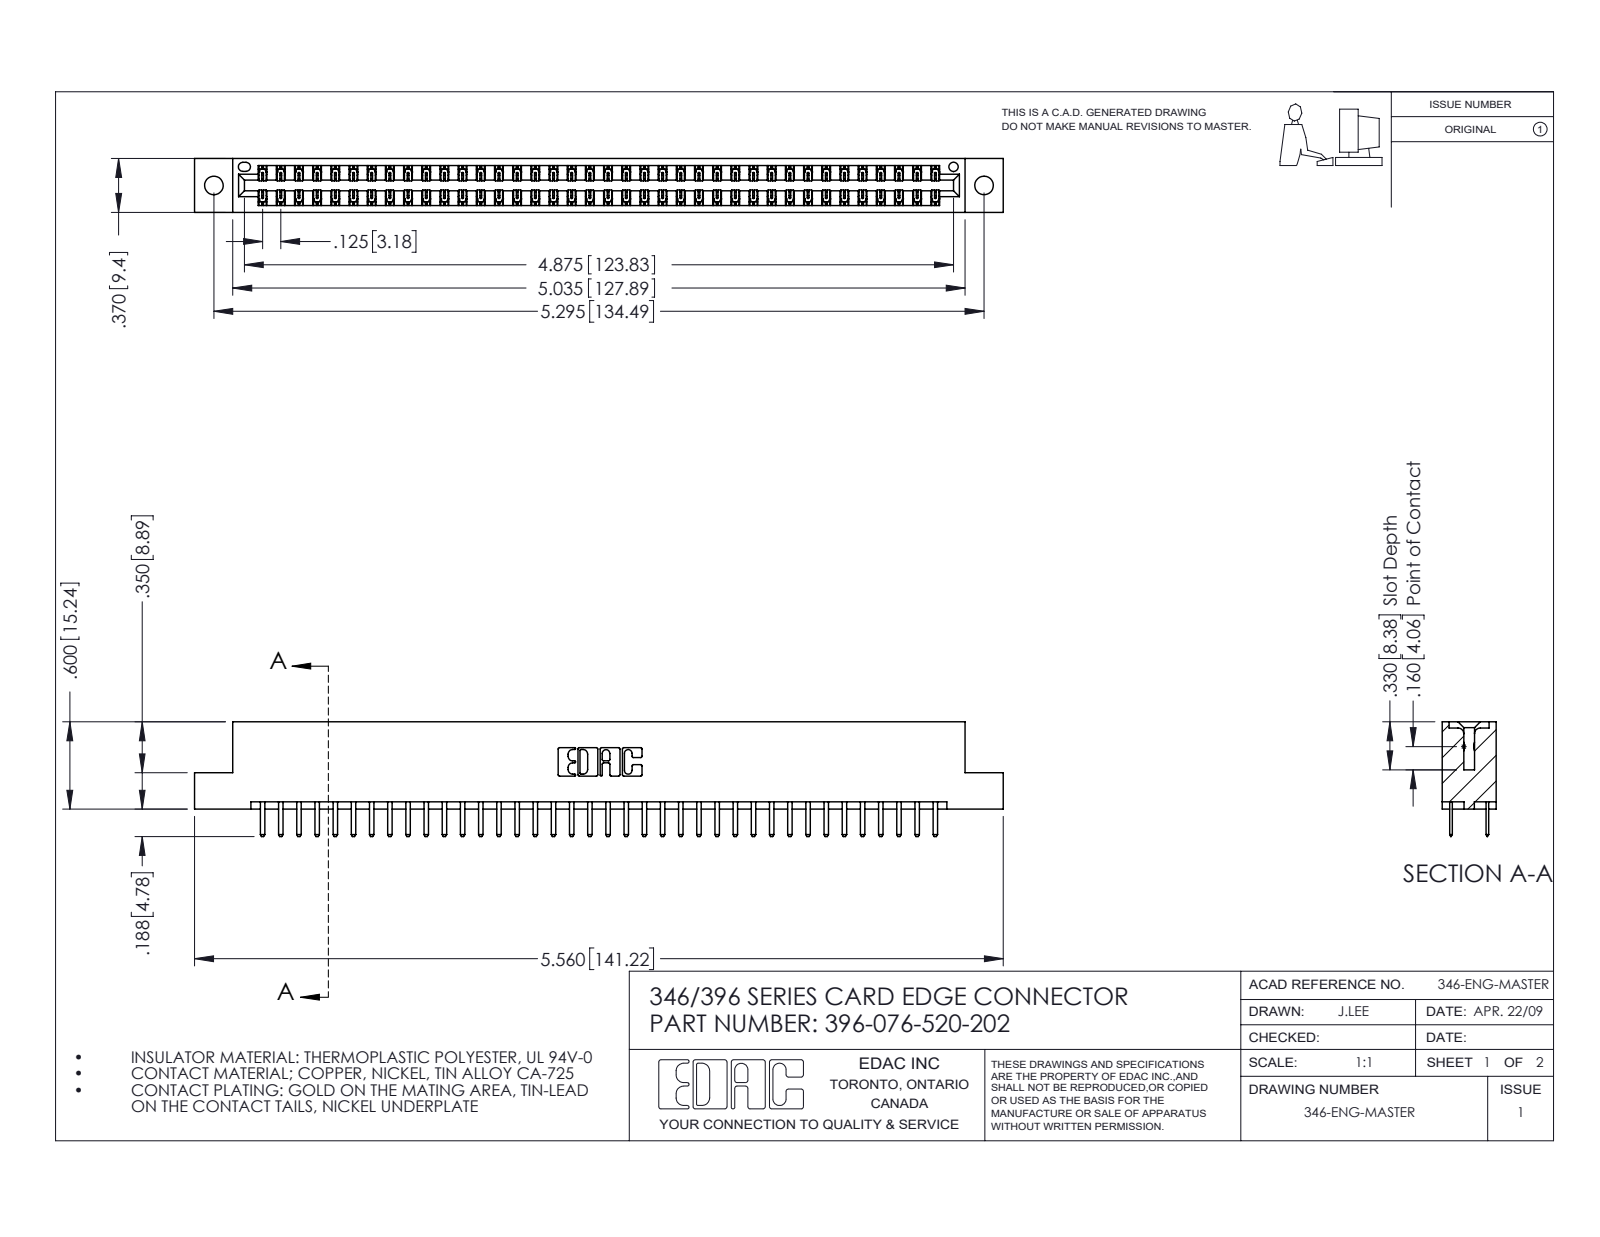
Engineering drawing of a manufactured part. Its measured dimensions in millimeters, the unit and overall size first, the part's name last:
Units: millimetres
Overall size (bounding box): 141.2 × 20 × 9.4
Round holes (diameter × count): ⌀3.3 ×2, ⌀1.6 ×1
Partial cylindrical surfaces — rounded edges, fillets, slot ends (radius × count): R0.2 ×114, R0.3 ×80, R0.3 ×22, R0.2 ×6, R0.8 ×6, R0.7 ×3, R0.4 ×2, R0.6 ×2
Main face-to-face distances: 1.2, 8.2, 6.4, 9.4, 7, 1.8, 7.6, 0.6, 3.8, 5.6
Hole centre spacings: 6.2, 129.2, 134.5
Volume: 13 700 mm³ · Surface area: 18 380 mm²
Bodies: 77 solids, 4378 faces (2888 planar, 1490 cylindrical, 0 other)
Part name (STEP PRODUCT): 396-076-520-202; 345-292-001_345-293-120; 346 Part_Flush Mounting Lugs - 0.128 Dia
STEP written by: SolidWorks 2016 (CONFIG_CONTROL_DESIGN)
